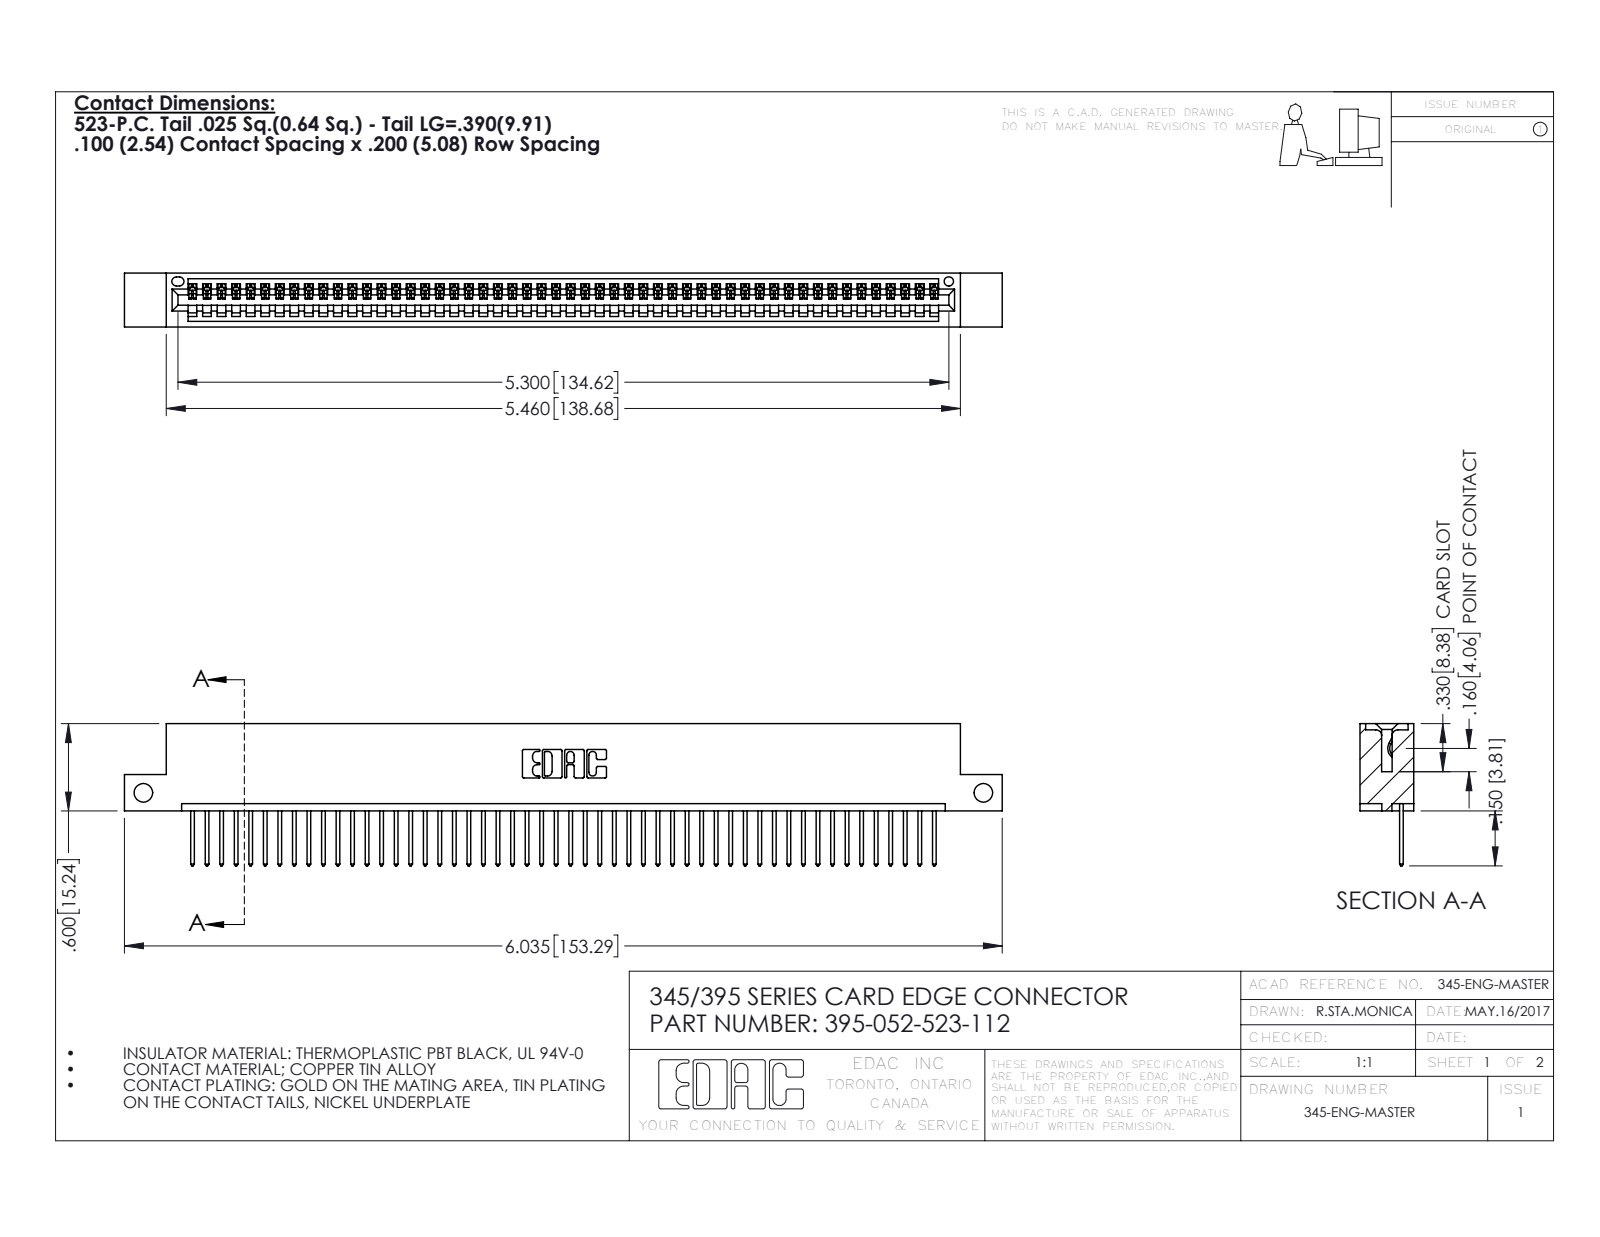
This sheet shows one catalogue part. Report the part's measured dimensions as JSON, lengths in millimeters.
{"part_name": "345-292-001_345-293-123; 395-052-523-112; 345 Part_Flush Mounting Lugs - Side Mount", "step_written_by": "SolidWorks 2016 (CONFIG_CONTROL_DESIGN)", "units": "millimeters", "bodies": {"solids": 53, "faces": 3142, "planar": 2160, "cylindrical": 982, "other": 0}, "overall_size": [153.3, 24.8, 9.4], "volume_mm3": 14500, "surface_area_mm2": 19370, "round_holes": [[3.3, 2], [1.6, 1]], "partial_cylinders_radius": [[0.2, 104], [0.3, 104], [0.3, 22], [0.2, 6], [0.8, 6], [0.7, 3], [0.8, 2], [1, 2]], "face_to_face_distances": [7.6, 1.8, 9.4, 5.1, 2.5, 6.9, 0.6, 5.7, 3.8, 1.8], "hole_center_spacings": [146.7]}
